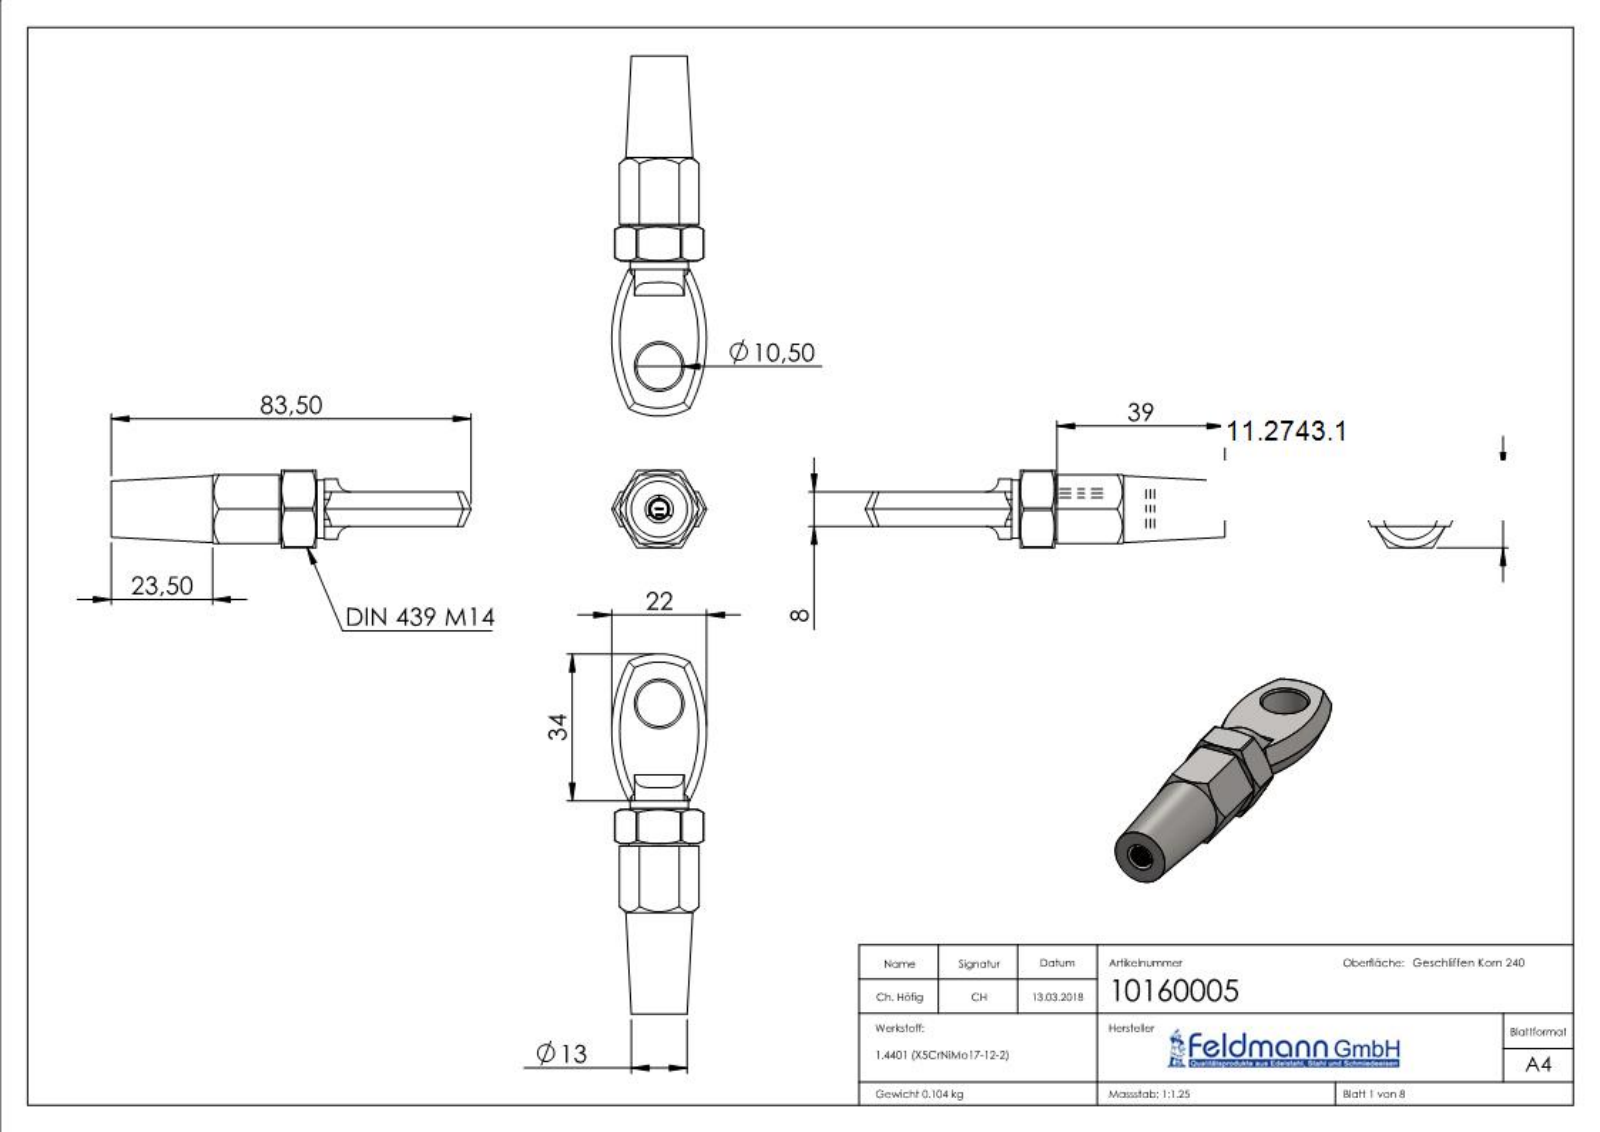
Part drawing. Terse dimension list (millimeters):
name: 1016000X Teil4_10160005 Teil3; 10160005; 1016000X Teil3_10160003 Teil3 Keyshot; 1016000X Teil1_10160005 Teil1 (+3 more)
written by: SolidWorks 2015 (CONFIG_CONTROL_DESIGN)
unit: mm
bodies: 8 solids, 561 faces (134 planar, 140 cylindrical, 287 other)
size: 83.5 × 22 × 18
volume: 12 943 mm³; area: 8 759 mm²
holes: 1× ⌀4.05, 1× ⌀4.5, 1× ⌀6.5, 1× ⌀8.2, 1× ⌀10.5, 1× ⌀12
bosses: 1× ⌀14, 1× ⌀13.5, 1× ⌀8
rounds: 6× R0.5, 4× R10, 2× R3
face distances: 8, 1, 17, 16, 12, 4, 18, 13, 5, 47.5
